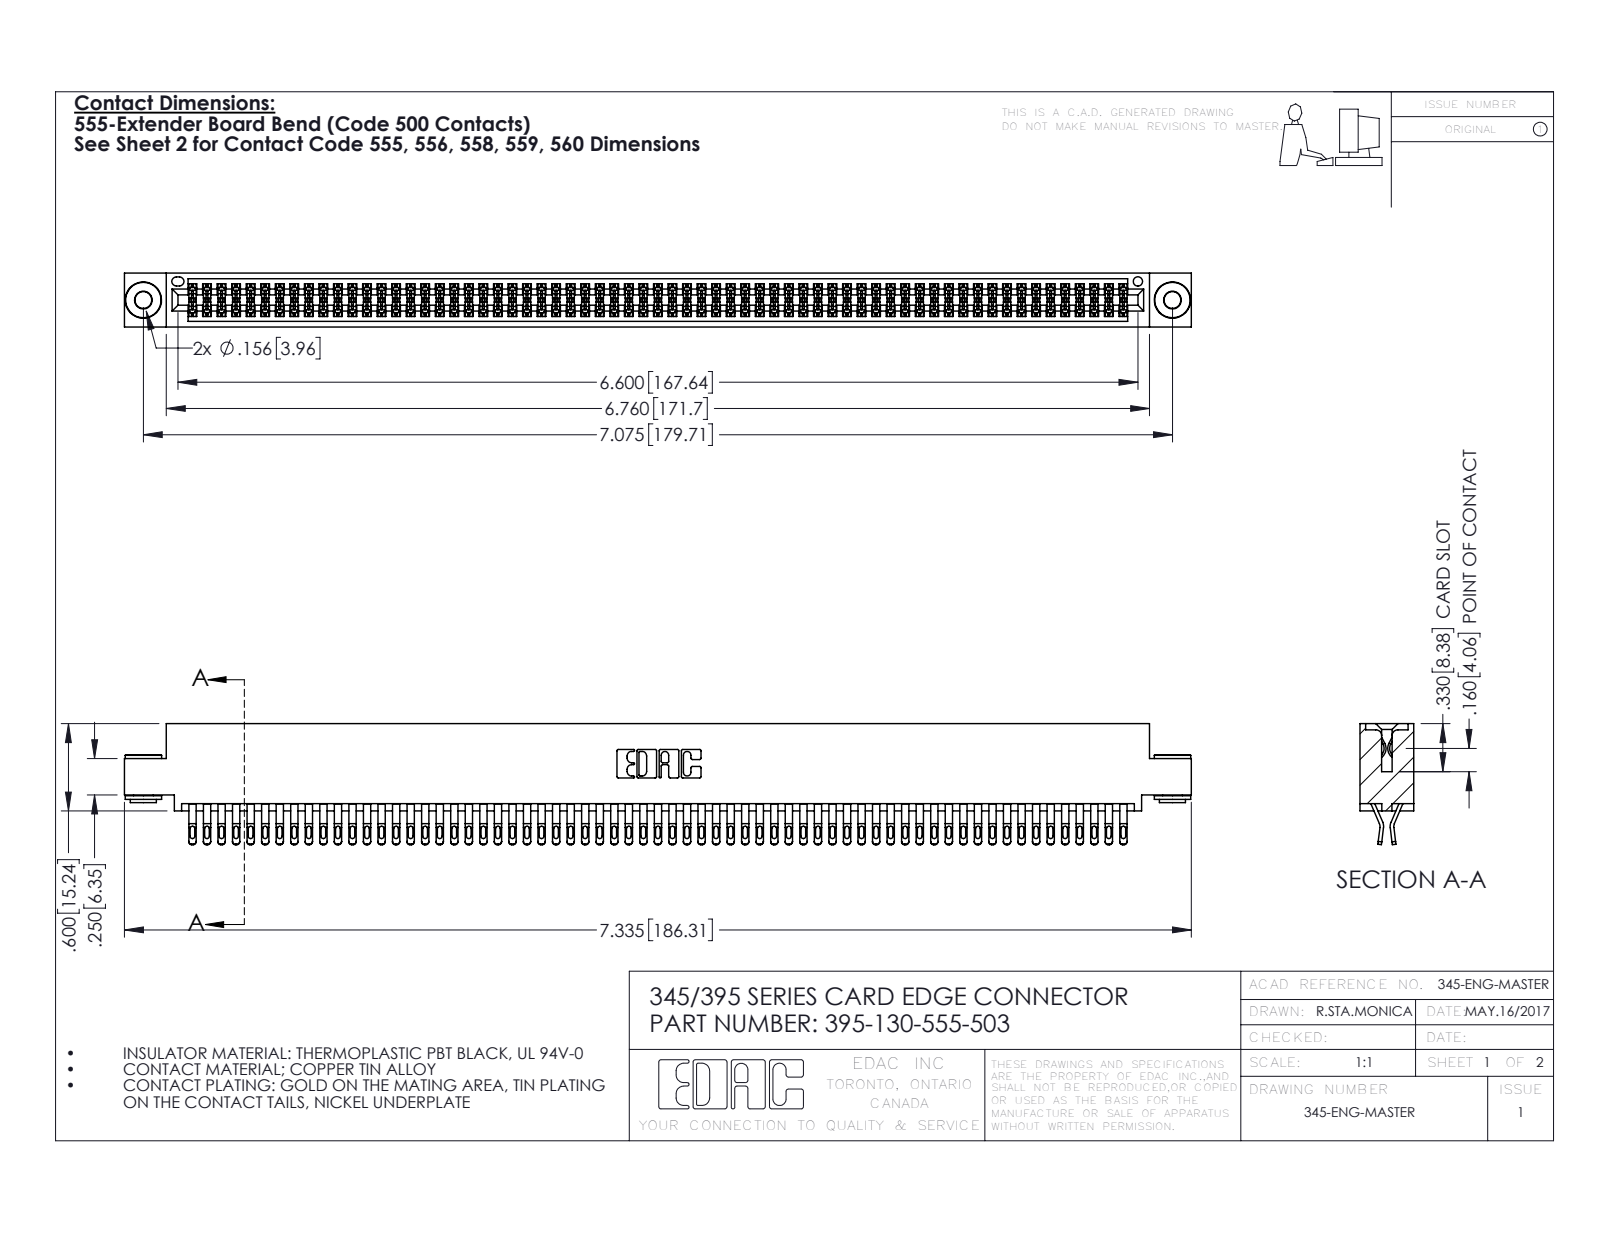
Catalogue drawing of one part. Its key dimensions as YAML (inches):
part_name: "345 Part_0.110 Offset - 0.156 Dia-TH; 395-130-555-503; 345-292-001_555 Tail; 345-250-002_345-250-002-102"
step_written_by: "SolidWorks 2016 (CONFIG_CONTROL_DESIGN)"
units: inches
bodies: {solids: 133, faces: 7448, planar: 4124, cylindrical: 3316, other: 8}
overall_size: [7.335, 0.832, 0.37]
volume: 1.137
surface_area: 45.88
round_holes:
  - {diameter: 0.116, count: 2}
  - {diameter: 0.156, count: 2}
  - {diameter: 0.064, count: 1}
round_bosses_or_shafts:
  - {diameter: 0.25, count: 2}
  - {diameter: 0.18, count: 2}
  - {diameter: 0.136, count: 2}
partial_cylinders:
  - {radius: 0.016, count: 325}
  - {radius: 0.02, count: 260}
  - {radius: 0.006, count: 195}
  - {radius: 0.01, count: 22}
  - {radius: 0.007, count: 6}
  - {radius: 0.031, count: 6}
  - {radius: 0.026, count: 3}
  - {radius: 0.01, count: 2}
face_to_face_distances: [0.072, 0.298, 0.025, 0.37, 0.2, 0.098, 0.272, 0.225, 0.175, 0.149]
hole_center_spacings: [0.27, 6.839, 7.075]
